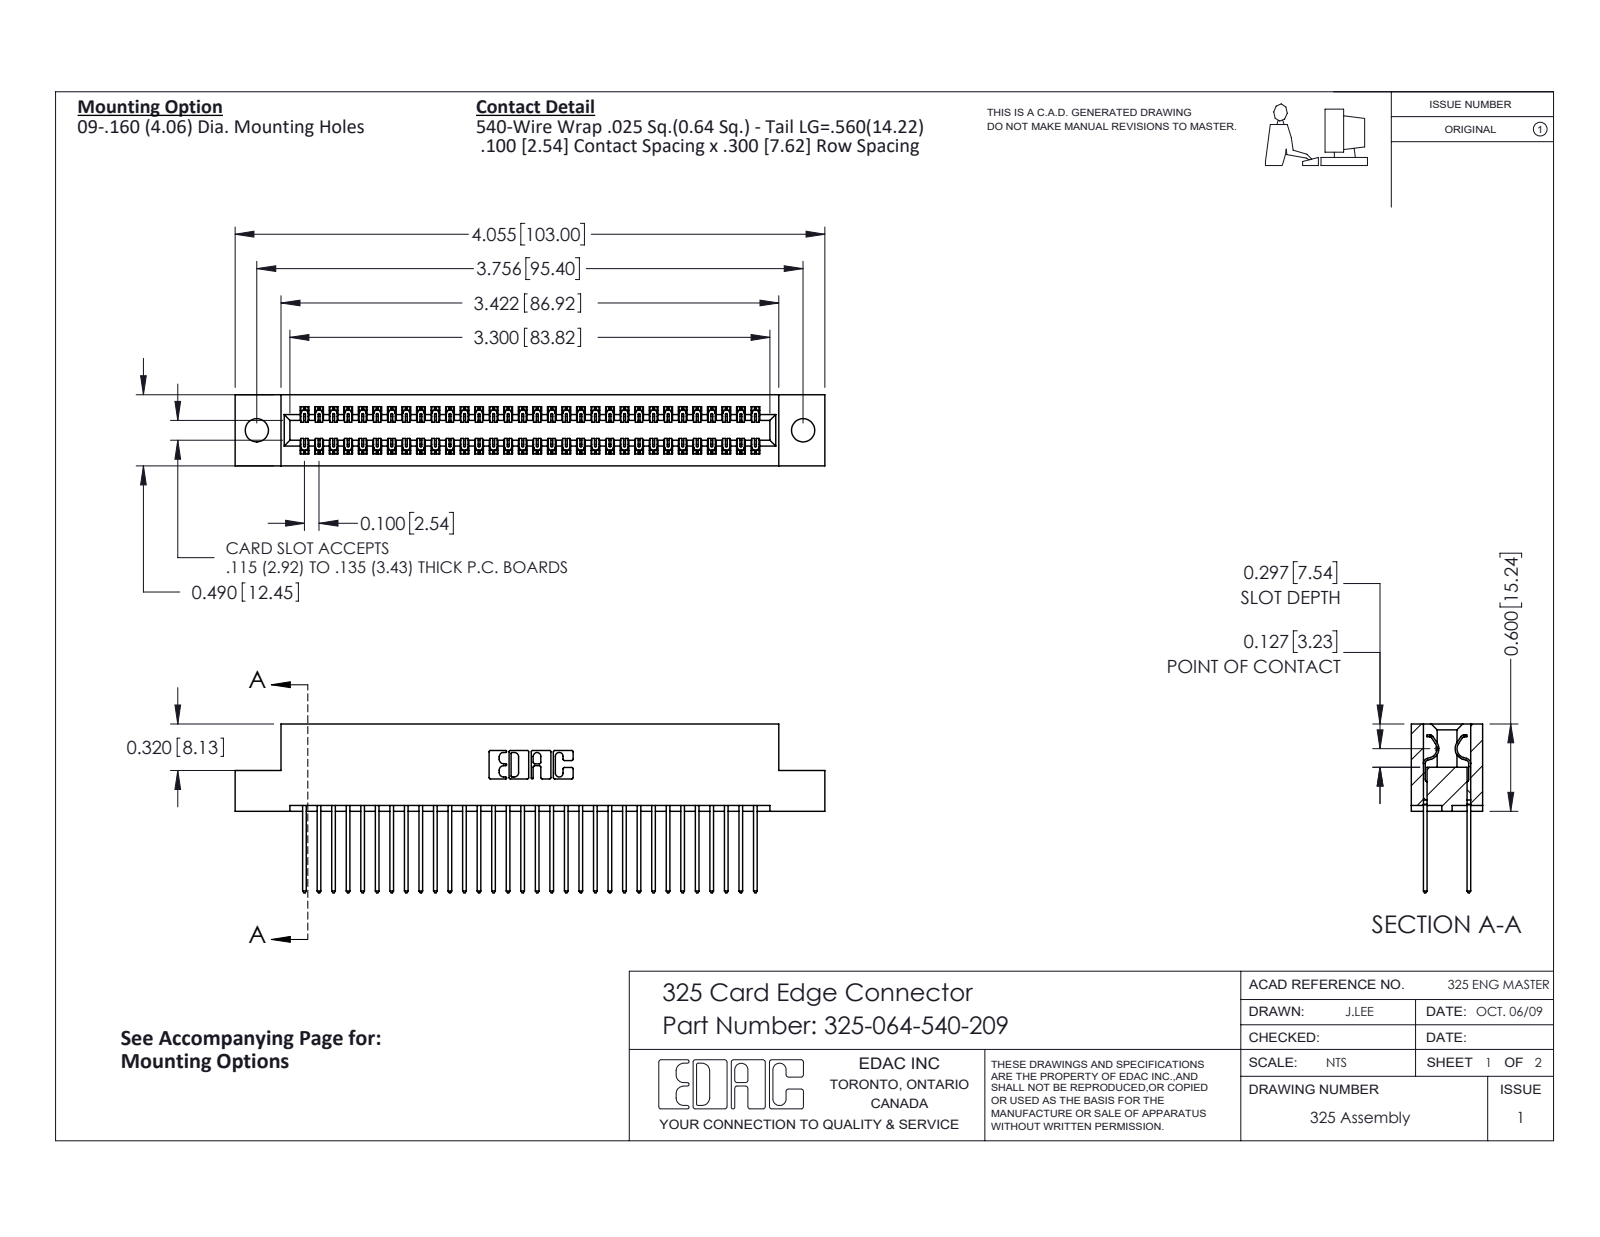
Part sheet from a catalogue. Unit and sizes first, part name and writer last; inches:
Units: inches
Overall size (bounding box): 4.055 × 1.16 × 0.49
Round holes (diameter × count): ⌀0.16 ×2
Partial cylindrical surfaces — rounded edges, fillets, slot ends (radius × count): R0.006 ×96, R0.01 ×64, R0.01 ×22, R0.007 ×6, R0.031 ×6, R0.026 ×3, R0.014 ×2, R0.022 ×2
Main face-to-face distances: 0.083, 0.407, 0.3, 0.107, 0.383, 0.025, 0.49, 0.325, 0.275, 0.04
Hole centre spacings: 3.756
Volume: 0.807 in³ · Surface area: 26.1 in²
Bodies: 65 solids, 3442 faces (2374 planar, 1068 cylindrical, 0 other)
Part name (STEP PRODUCT): 325-064-540-209; 325 Part_.160 TH; 325-292-001_325-293-140
STEP written by: SolidWorks 2016 (CONFIG_CONTROL_DESIGN)
